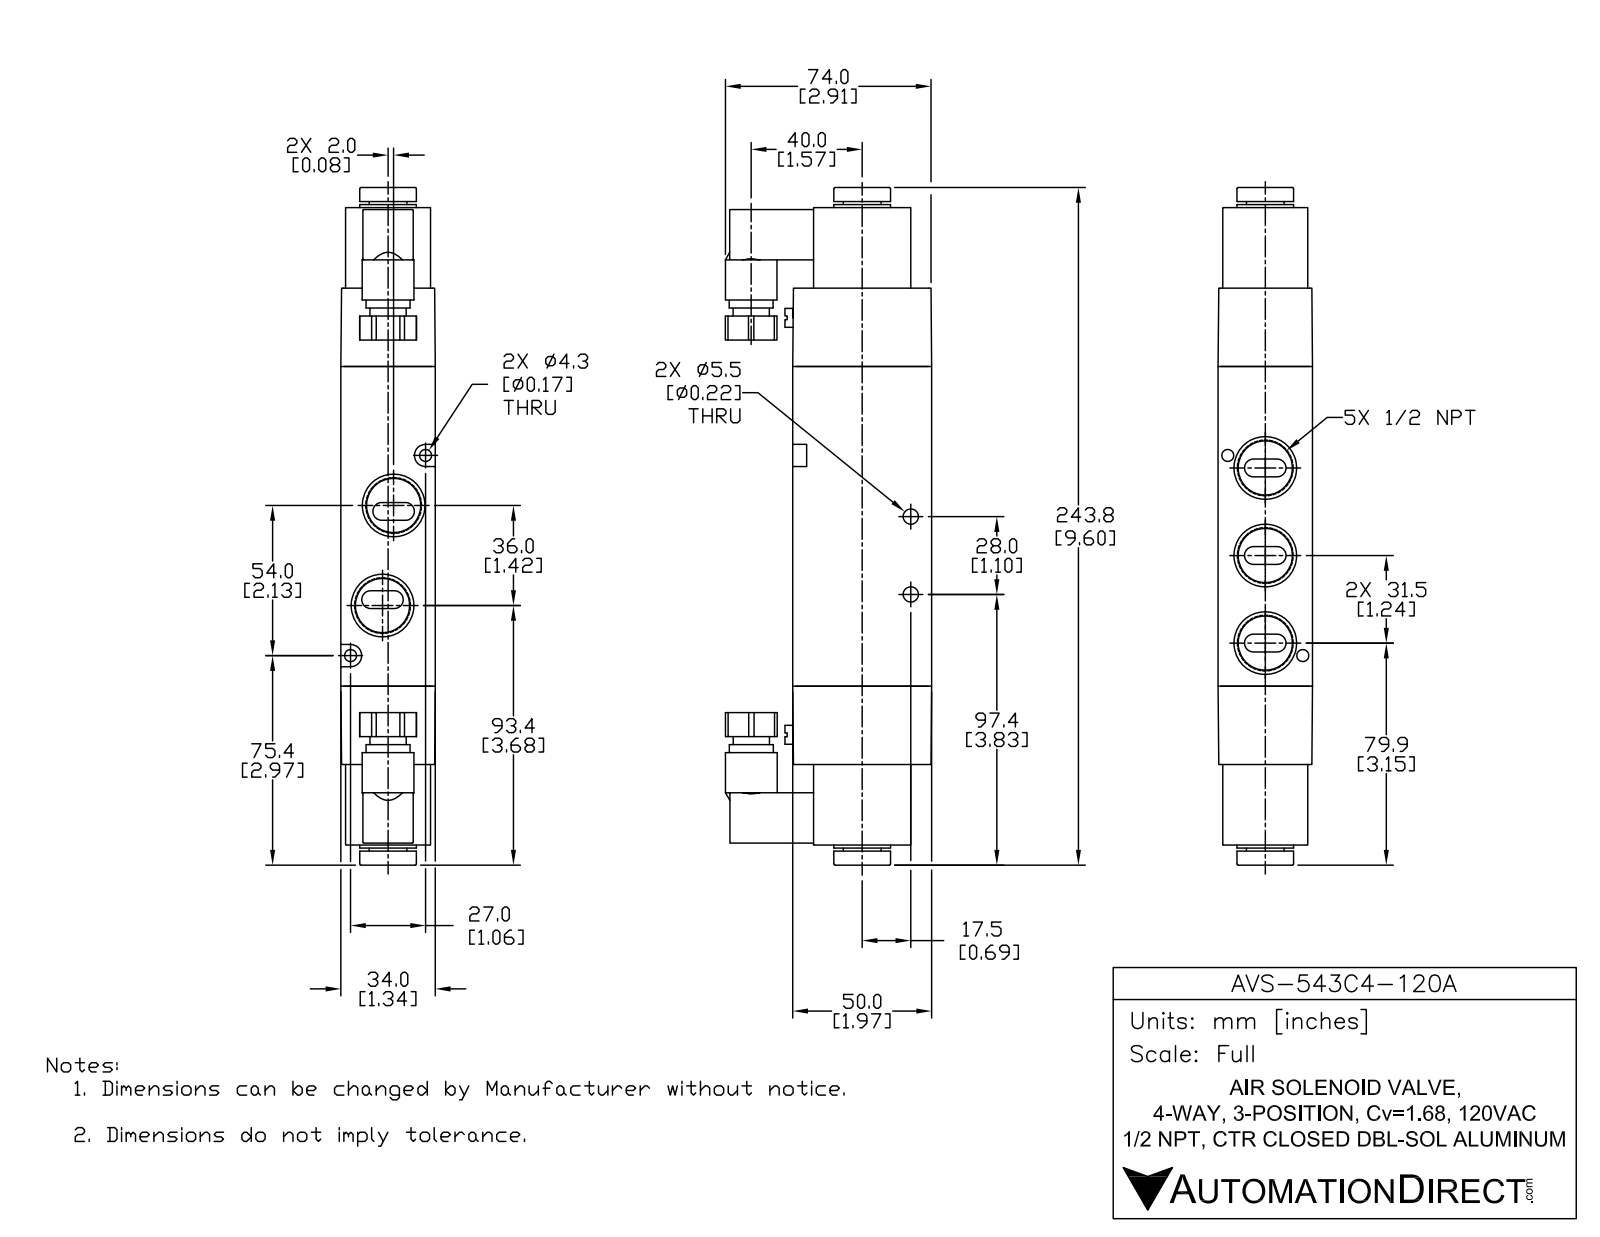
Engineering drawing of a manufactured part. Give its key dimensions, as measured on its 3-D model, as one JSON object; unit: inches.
{"part_name": "AVS-543C4-120A", "step_written_by": "SolidWorks 2015 (CONFIG_CONTROL_DESIGN)", "units": "inches", "bodies": {"solids": 5, "faces": 248, "planar": 111, "cylindrical": 103, "other": 34}, "overall_size": [9.598, 2.921, 1.339], "volume_in3": 21.74, "surface_area_in2": 100, "round_holes": [[0.703, 5], [0.169, 2], [0.217, 2], [0.366, 1]], "round_bosses_or_shafts": [[0.264, 2], [0.819, 1], [0.803, 1], [0.732, 1], [0.622, 1], [0.535, 1], [0.512, 1]], "partial_cylinders_radius": [[0.059, 18], [0.039, 10], [0.126, 10], [0.157, 2]], "face_to_face_distances": [1.339, 4.528, 1.969, 1.416, 1.11, 1.265, 2.046, 0.313, 1.026, 0.713], "hole_center_spacings": [0.537, 0.56, 0.713, 0.841, 1.24, 1.514, 1.95, 2.212]}
